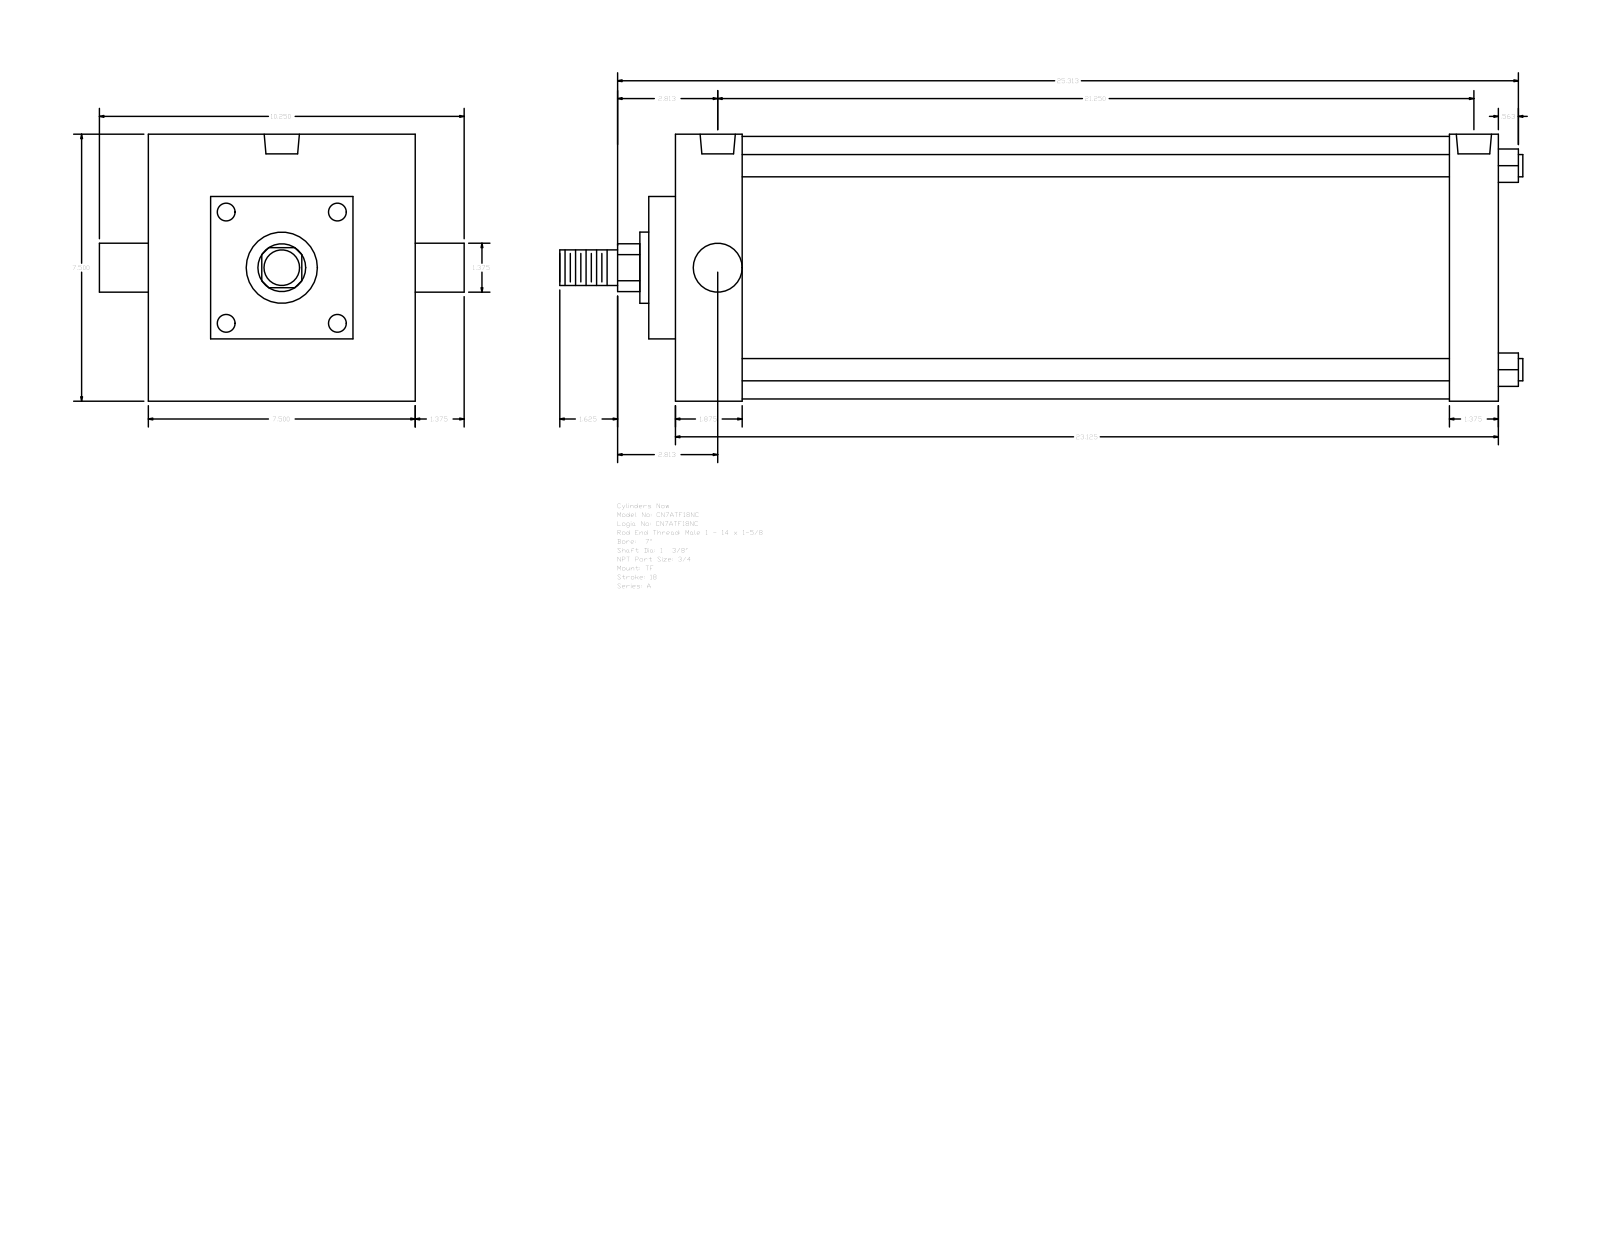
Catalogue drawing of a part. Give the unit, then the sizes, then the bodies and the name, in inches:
Units: inches
Overall size (bounding box): 27.063 × 10.25 × 7.5
Round holes (diameter × count): ⌀0.594 ×3, ⌀0.989 ×2
Round bosses / shafts (diameter × count): ⌀0.625 ×4, ⌀1.375 ×2, ⌀7.375 ×1, ⌀2 ×1, ⌀1 ×1
Partial cylindrical surfaces — rounded edges, fillets, slot ends (radius × count): R0.672 ×1
Main face-to-face distances: 7.5, 23.125, 0.75, 23.875, 2.625, 1.875, 21.25, 22.5, 21.75, 19.875
Hole centre spacings: 0.219, 21.031, 20.812, 21.25
Bodies: 0 solids, 89 faces (65 planar, 24 cylindrical, 0 other)
Part name (STEP PRODUCT): A_TF__0700_1.375
STEP written by: GSSL Pune (CONFIG_CONTROL_DESIGN)
